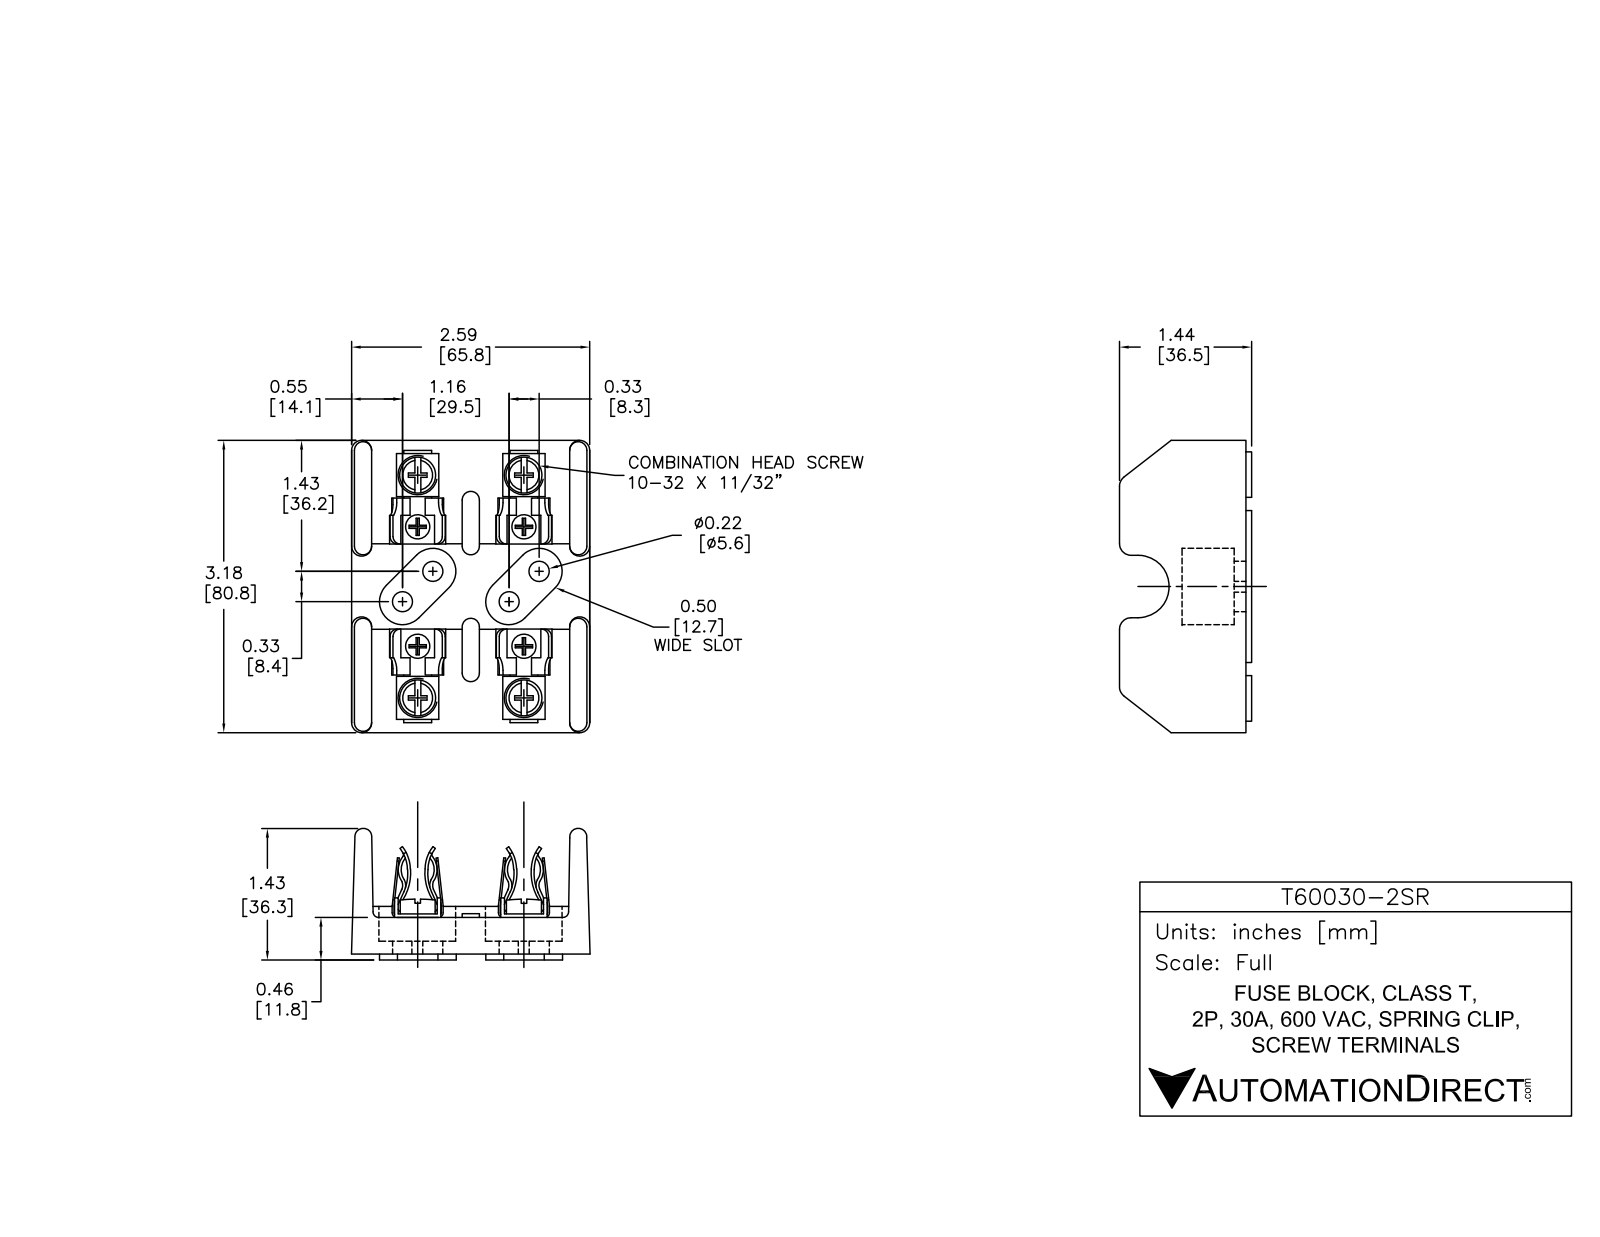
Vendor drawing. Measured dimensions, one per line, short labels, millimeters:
name: T60030-2SR
written by: SolidWorks 2019 (AUTOMOTIVE_DESIGN)
unit: mm
bodies: 9 solids, 396 faces (188 planar, 172 cylindrical, 36 other)
size: 80.8 × 65.8 × 36.5
volume: 80 980 mm³; area: 32 770 mm²
holes: 4× ⌀5.6, 4× ⌀5.6
bosses: 4× ⌀12, 4× ⌀9.5
rounds: 23× R3.2, 16× R6.4, 8× R5.1, 4× R5.3, 4× R8.4, 2× R6.2, 2× R7.5
face distances: 10.7, 6.4, 59.5, 65.8, 12.7, 2, 1.3, 53.1, 14, 12
hole spacings: 27.1, 29.5, 35.4, 11.9, 36.8, 43, 43.3, 48.7
